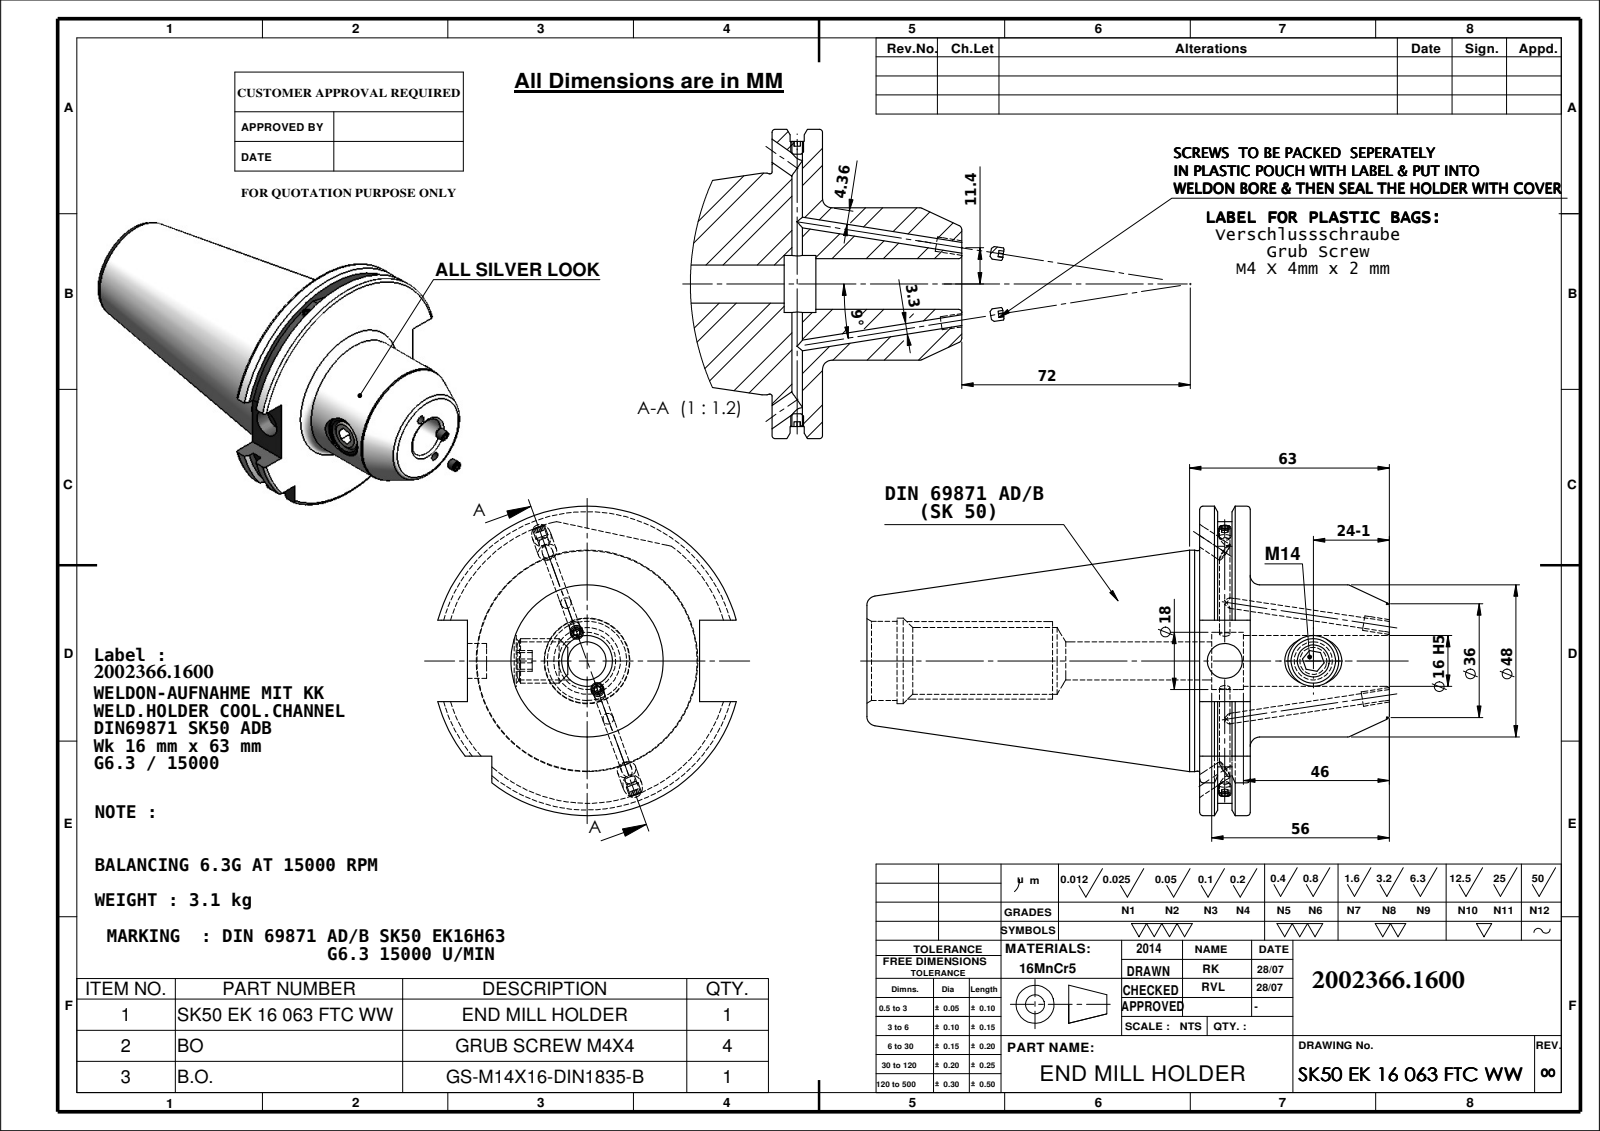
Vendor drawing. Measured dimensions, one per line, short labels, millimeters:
name: SK50 EK 16 063 FTC WW; Copy of M4X4_DIN 913 - M4 x 4-N; M14X16_ISO 4026 - M12 x 12-N
written by: SolidWorks 2009 (CONFIG_CONTROL_DESIGN)
unit: mm
bodies: 6 solids, 206 faces (71 planar, 69 cylindrical, 66 other)
size: 178.07 × 97.5 × 94.05
volume: 394 948 mm³; area: 54 296 mm²
holes: 3× ⌀3.3, 2× ⌀6, 2× ⌀12, 2× ⌀16, 1× ⌀11, 1× ⌀18, 1× ⌀21, 1× ⌀25, 1× ⌀27
bosses: 4× ⌀4, 1× ⌀69.85, 1× ⌀69.45, 1× ⌀48, 1× ⌀14
rounds: 1× R44.9, 1× R48.75
face distances: 15.9, 59.8, 43.9, 10.15, 5.75, 49.65, 5.66, 4.49, 10.24, 54.14
hole spacings: 27.9
